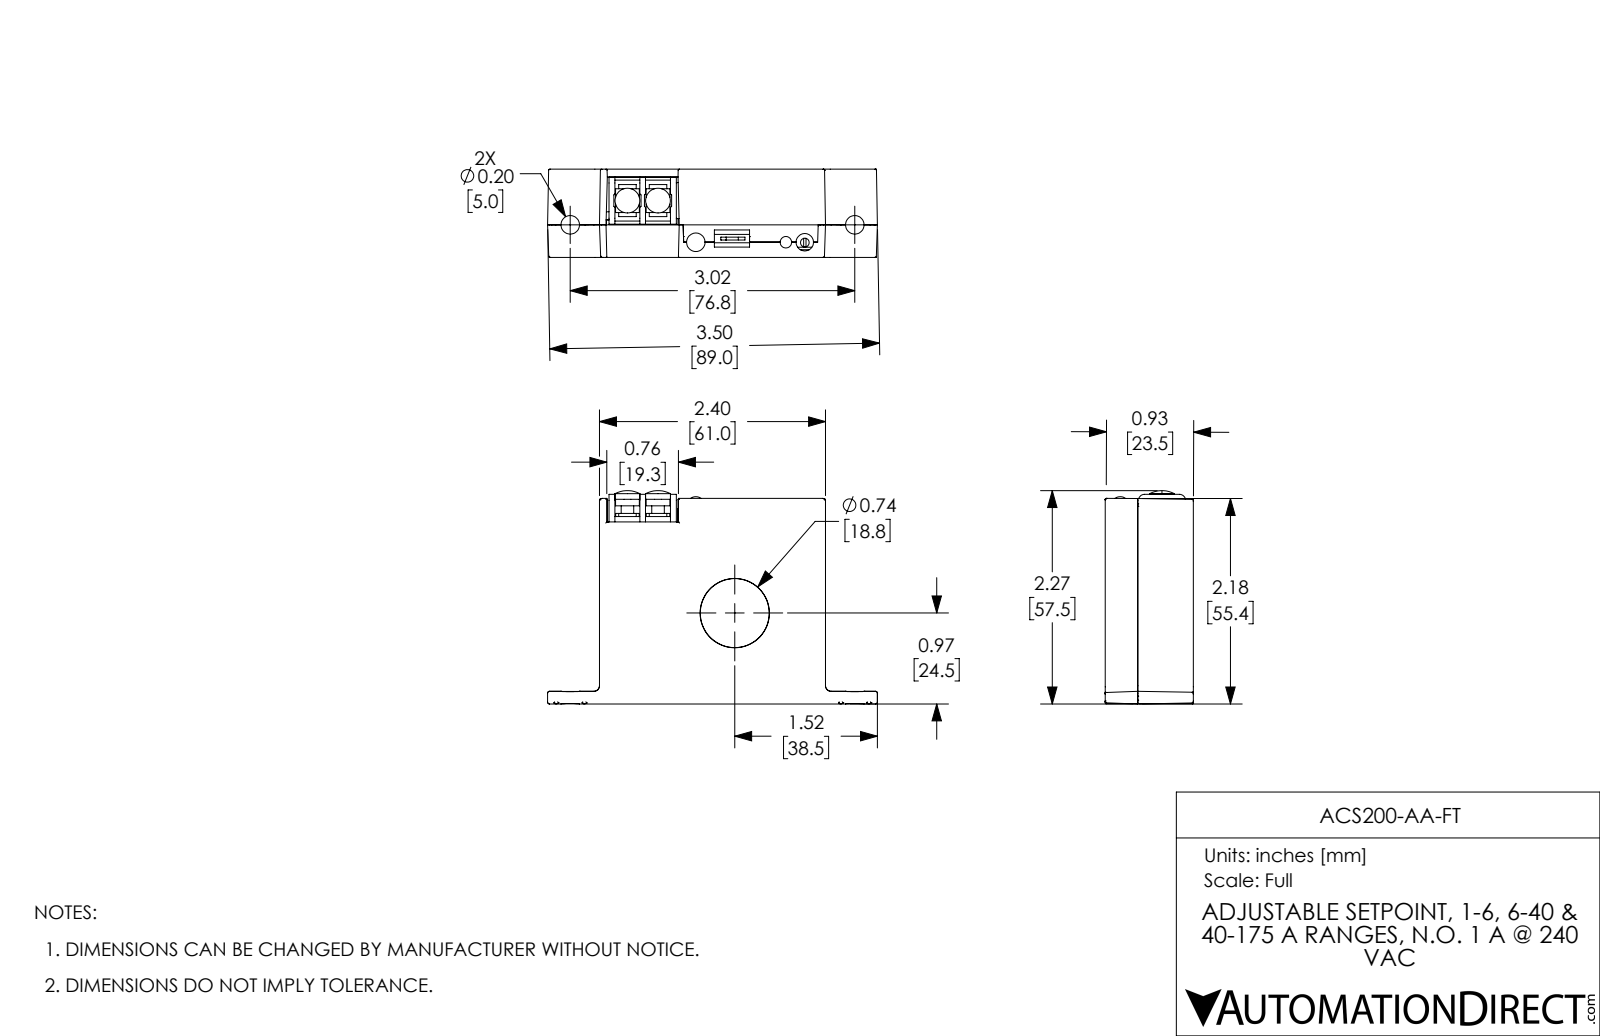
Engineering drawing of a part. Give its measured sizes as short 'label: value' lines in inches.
name: ACS200-AA-FT
written by: SolidWorks 2017 (AUTOMOTIVE_DESIGN)
unit: in
bodies: 8 solids, 550 faces (360 planar, 126 cylindrical, 64 other)
size: 3.504 × 2.265 × 0.937
volume: 1.893 in³; area: 53.16 in²
holes: 4× ⌀0.045, 3× ⌀0.197, 2× ⌀0.147, 1× ⌀0.122, 1× ⌀0.185, 1× ⌀0.82
bosses: 4× ⌀0.043, 2× ⌀0.263, 2× ⌀0.134, 1× ⌀0.807, 1× ⌀0.234, 1× ⌀0.194, 1× ⌀0.093
rounds: 20× R0.012, 12× R0.02, 8× R0.03, 4× R0.059, 2× R0.008, 2× R0.063
face distances: 0.083, 0.854, 0.937, 0.772, 0.442, 0.349, 0.413, 0.266, 0.33, 0.064
hole spacings: 2.151, 3.535, 0.201, 0.325, 0.563, 0.598, 0.66, 0.755
